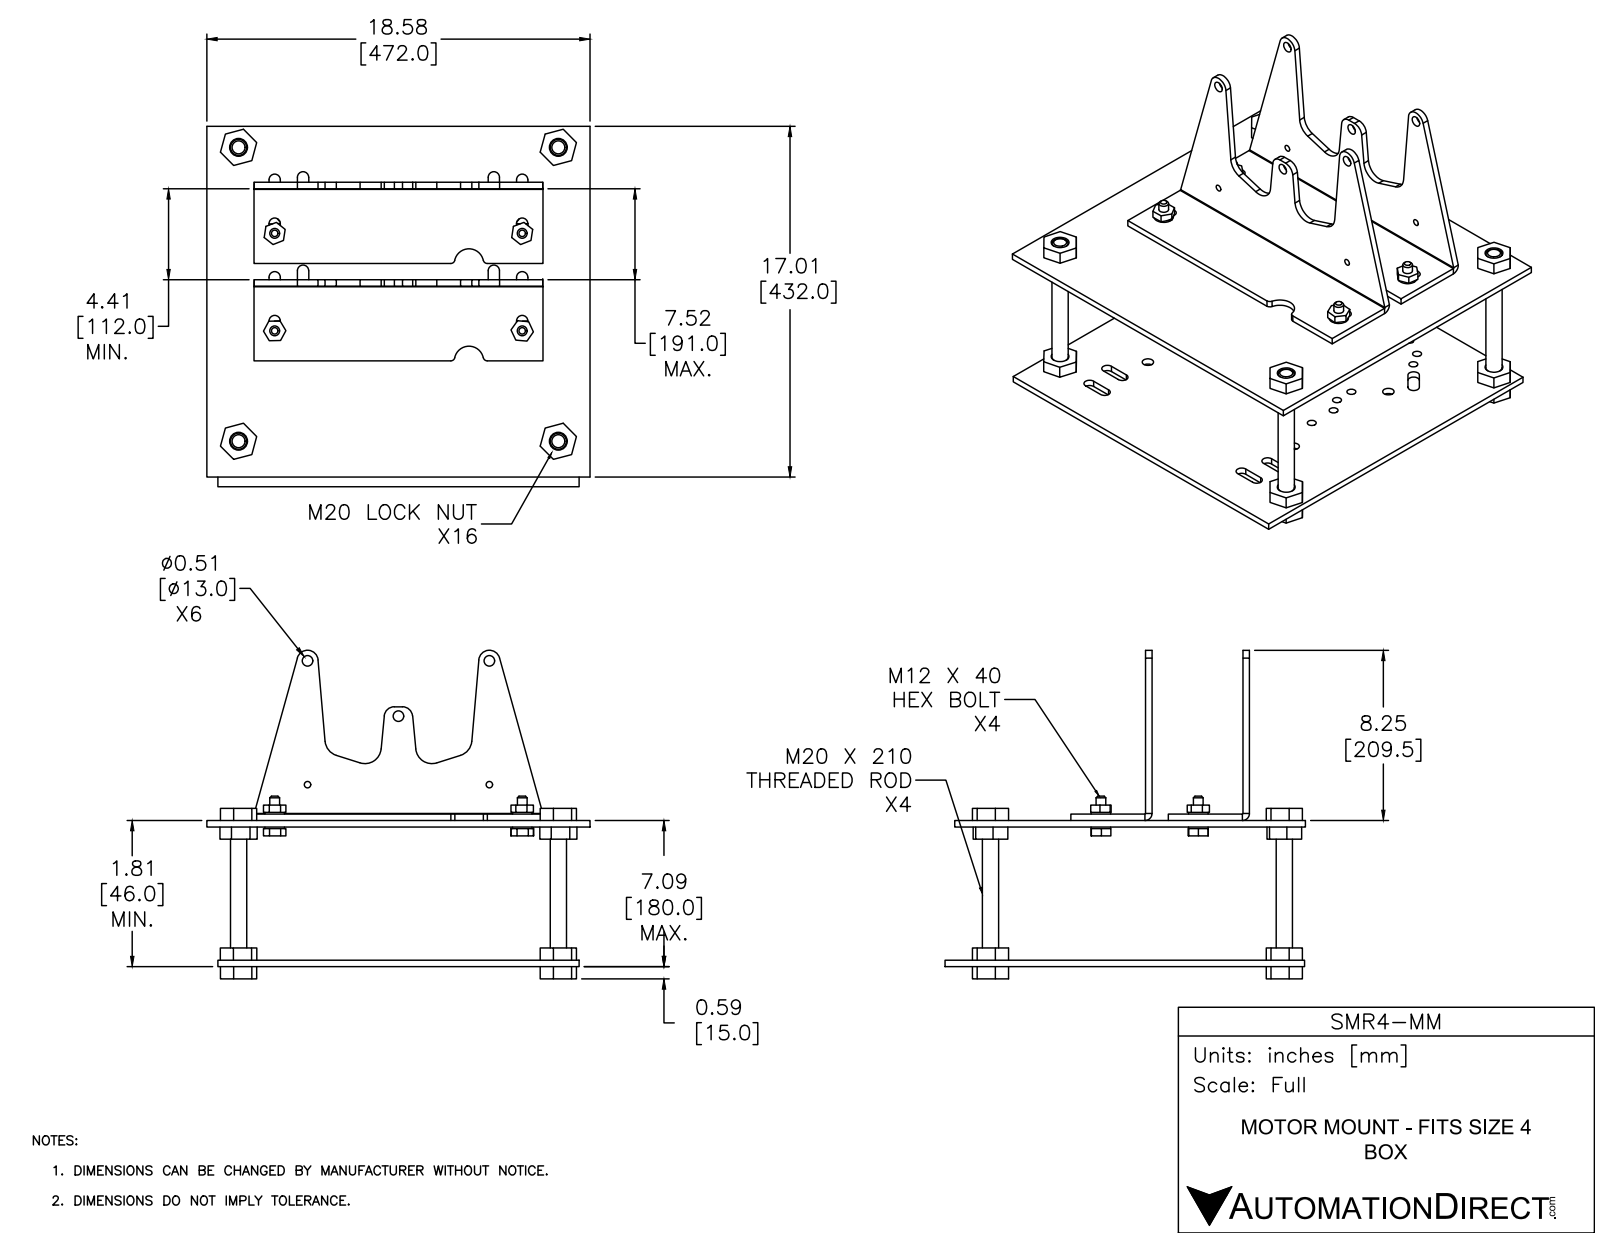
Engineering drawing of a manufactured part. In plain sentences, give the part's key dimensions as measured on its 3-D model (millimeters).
The part is named "SMR4-MM". Its 3-D file was written by "SolidWorks 2016 (AUTOMOTIVE_DESIGN)". It is 40 solids with 630 faces: 302 planar, 236 cylindrical and 92 other. Overall it measures 472 by 444 by 404.5 millimeters. Its volume is 4 808 000 cubic millimeters and its surface area 1 303 000 square millimeters. Round holes: 12 of diameter 11, 4 of diameter 12, 4 of diameter 14, 4 of diameter 20, 4 of diameter 20.5, 4 of diameter 21, 3 of diameter 9.5, 3 of diameter 13, 2 of diameter 8. Round bosses or shafts: 4 of diameter 24. Partial cylindrical surfaces (rounded edges, fillets, slot ends): 32 of radius 7, 4 of radius 5, 4 of radius 20, 2 of radius 0.74, 2 of radius 8.74, 2 of radius 12.5, 2 of radius 13, 2 of radius 18. The main face-to-face distances are 8, 172, 180, 164, 120, 188, 16, 112, 128, 15. The hole center spacings are 256.02, 57.87, 65.8, 190, 215, 250.82, 22.33, 22.74.
